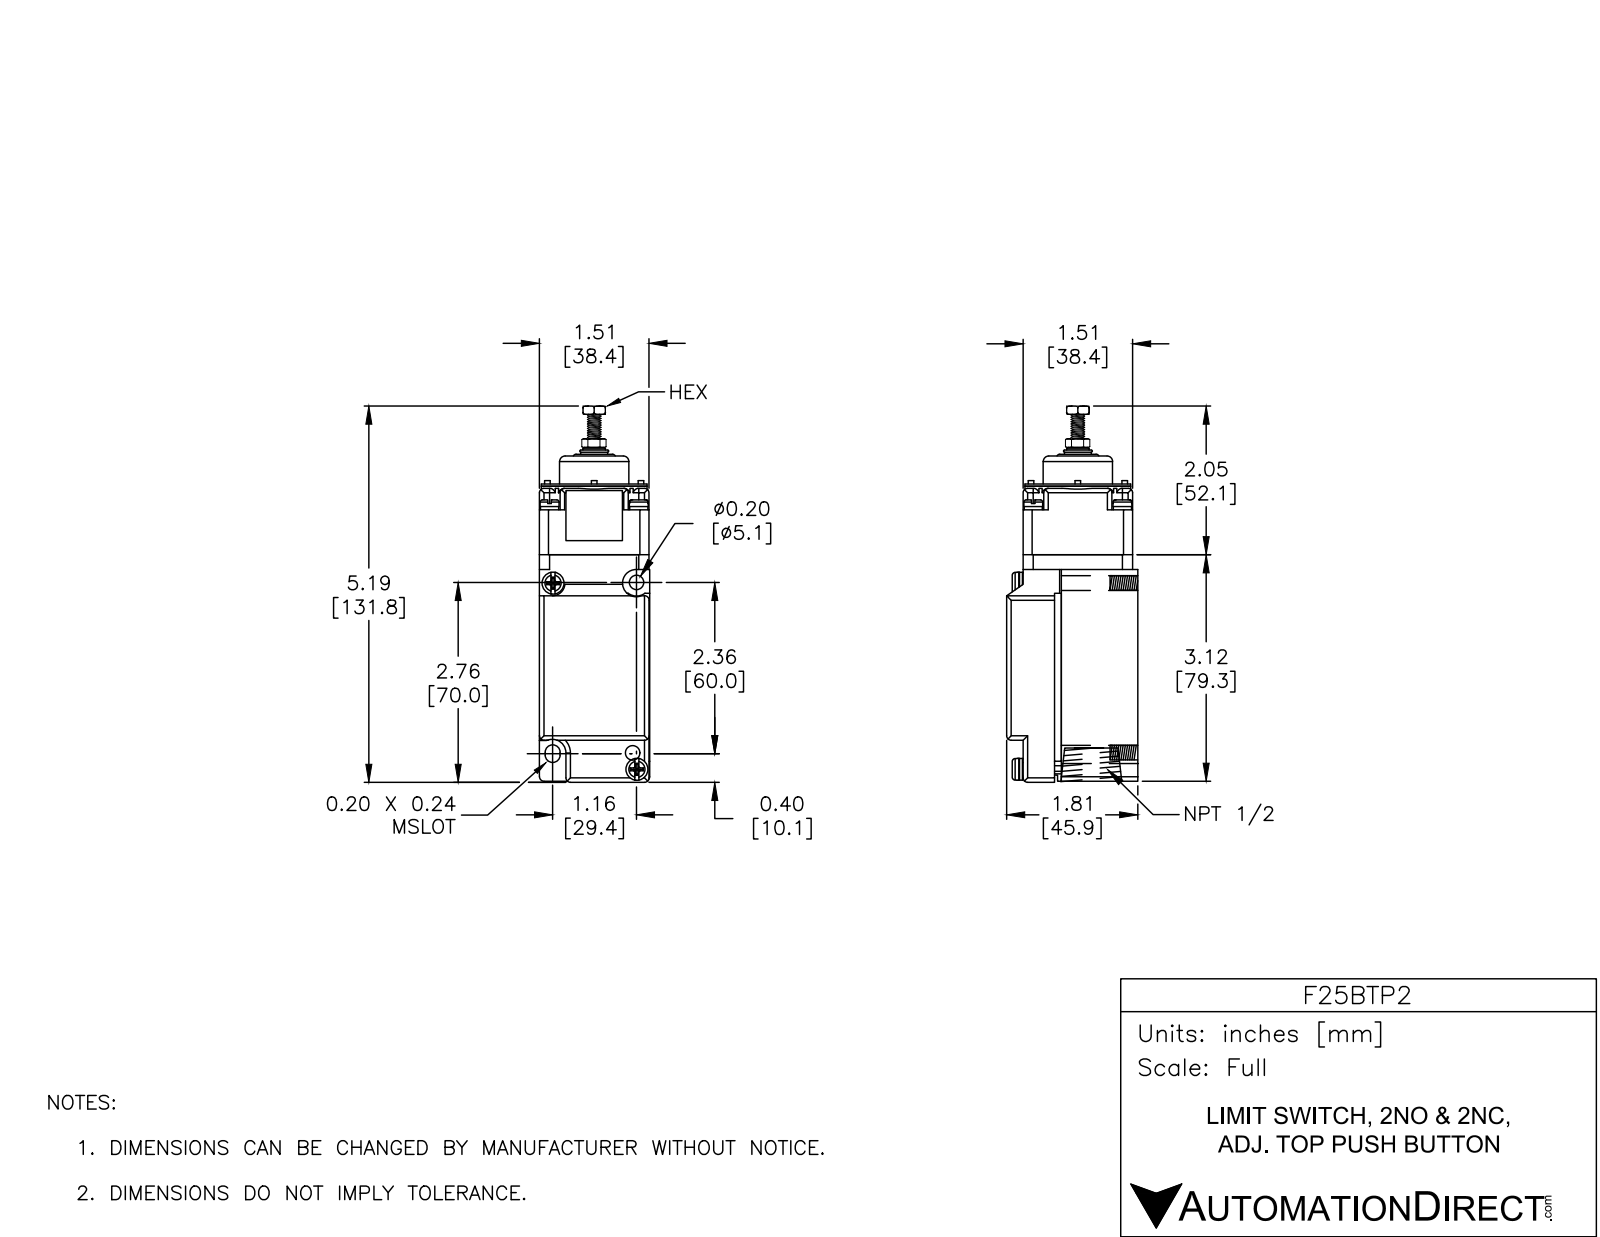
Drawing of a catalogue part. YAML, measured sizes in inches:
part_name: "F25BTP2"
step_written_by: "SolidWorks 2018 (AUTOMOTIVE_DESIGN)"
units: inches
bodies: {solids: 16, faces: 799, planar: 268, cylindrical: 136, other: 395}
overall_size: [5.189, 1.809, 1.52]
volume: 9.997
surface_area: 75.77
round_holes:
  - {diameter: 0.077, count: 4}
  - {diameter: 0.177, count: 4}
  - {diameter: 0.19, count: 3}
  - {diameter: 0.2, count: 3}
  - {diameter: 0.096, count: 1}
  - {diameter: 0.23, count: 1}
  - {diameter: 0.92, count: 1}
  - {diameter: 1.054, count: 1}
round_bosses_or_shafts:
  - {diameter: 0.25, count: 5}
  - {diameter: 0.26, count: 4}
  - {diameter: 0.14, count: 4}
  - {diameter: 0.302, count: 2}
  - {diameter: 0.3, count: 2}
  - {diameter: 1.458, count: 1}
  - {diameter: 0.956, count: 1}
  - {diameter: 0.4, count: 1}
partial_cylinders:
  - {radius: 0.062, count: 21}
  - {radius: 0.03, count: 16}
  - {radius: 0.015, count: 8}
  - {radius: 0.062, count: 8}
  - {radius: 0.14, count: 4}
  - {radius: 0.145, count: 4}
  - {radius: 0.102, count: 2}
  - {radius: 0.188, count: 2}
face_to_face_distances: [0.094, 1.149, 1.055, 1.52, 0.945, 0.66, 0.754, 1.809, 1.51, 0.227]
hole_center_spacings: [1.403, 0.616, 0.646, 0.616, 0.87, 0.87, 0.913, 0.914]
